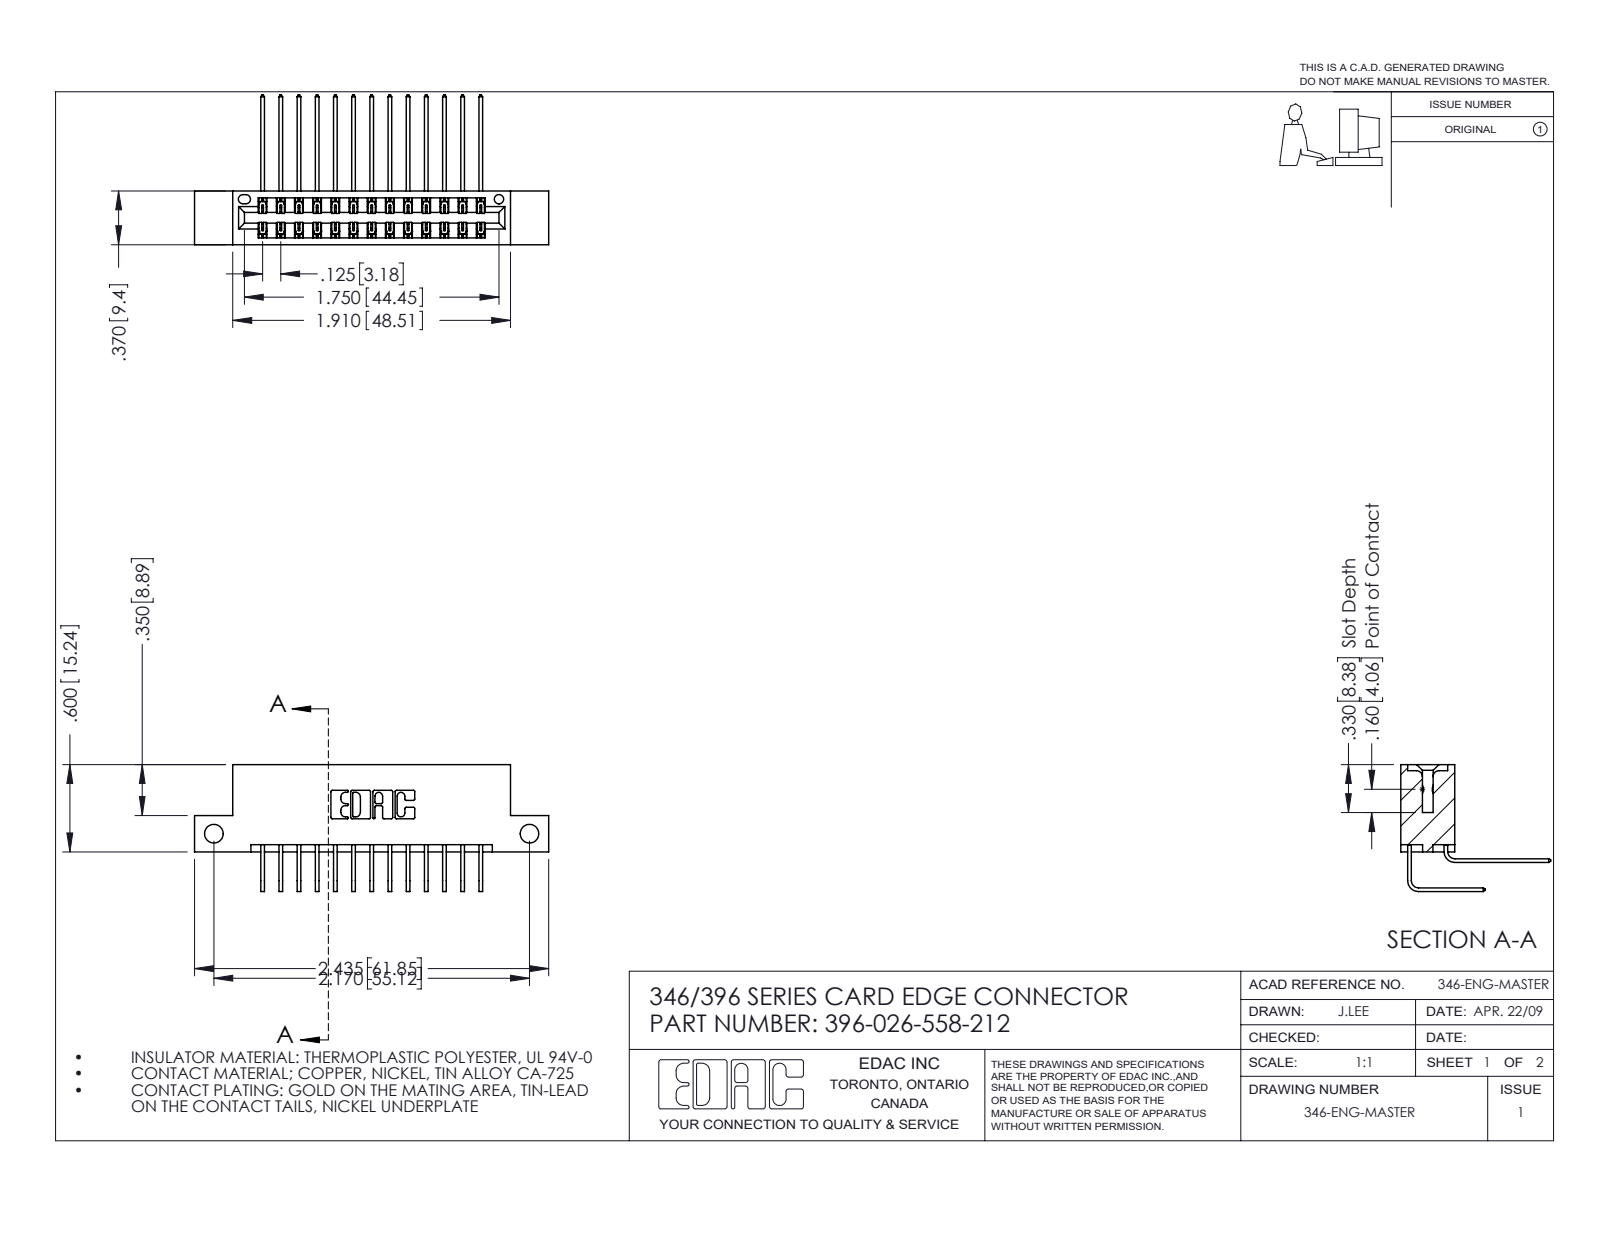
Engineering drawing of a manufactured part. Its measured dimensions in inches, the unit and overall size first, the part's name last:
Units: inches
Overall size (bounding box): 2.435 × 1.03 × 0.873
Round holes (diameter × count): ⌀0.128 ×2, ⌀0.064 ×1
Partial cylindrical surfaces — rounded edges, fillets, slot ends (radius × count): R0.006 ×39, R0.01 ×22, R0.007 ×6, R0.031 ×6, R0.026 ×3, R0.014 ×2, R0.022 ×2, R0.024 ×2
Main face-to-face distances: 0.322, 0.048, 0.25, 0.37, 0.025, 0.298, 0.072, 0.275, 0.148, 0.222
Hole centre spacings: 2.17
Volume: 0.358 in³ · Surface area: 12.7 in²
Bodies: 27 solids, 1526 faces (1038 planar, 488 cylindrical, 0 other)
Part name (STEP PRODUCT): 396-026-558-212; 345-292-001_558 559 Tail - 1; 345-292-001_558 Tail - 2; 346 Part_Flush Mounting Lugs - Side Mount
STEP written by: SolidWorks 2016 (CONFIG_CONTROL_DESIGN)
